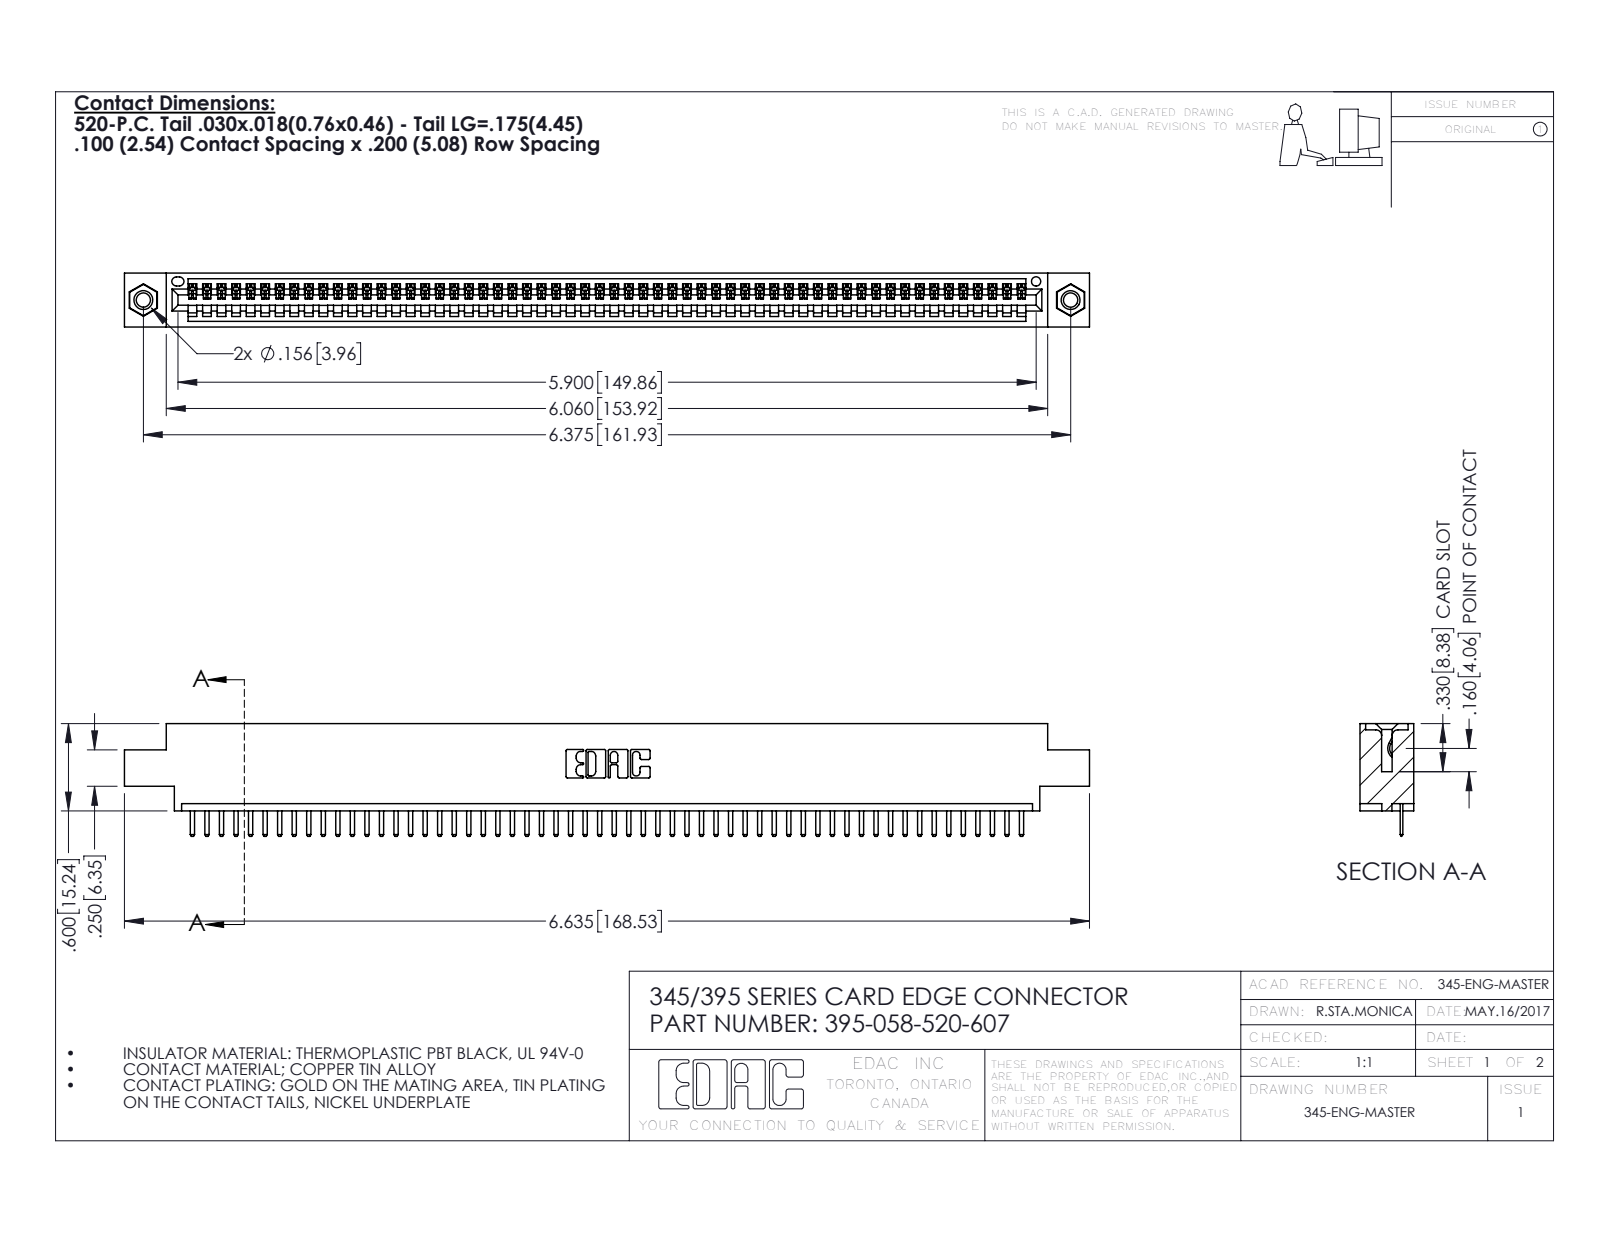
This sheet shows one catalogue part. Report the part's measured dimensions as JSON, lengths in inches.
{"part_name": "345-292-001_345-293-120; 345 Part_0.170 Offset - 0.156 Dia-TI; 345-250-001_345-250-005-103; 395-058-520-607", "step_written_by": "SolidWorks 2016 (CONFIG_CONTROL_DESIGN)", "units": "inches", "bodies": {"solids": 61, "faces": 3786, "planar": 2552, "cylindrical": 1218, "other": 16}, "overall_size": [6.635, 0.775, 0.37], "volume_in3": 0.967, "surface_area_in2": 32.37, "round_holes": [[0.098, 2], [0.125, 2], [0.156, 2], [0.064, 1]], "round_bosses_or_shafts": [[0.155, 2]], "partial_cylinders_radius": [[0.01, 118], [0.006, 116], [0.01, 22], [0.007, 6], [0.031, 6], [0.026, 3], [0.031, 2], [0.04, 2]], "face_to_face_distances": [0.072, 0.298, 0.37, 0.2, 0.098, 0.272, 0.025, 0.225, 0.072, 0.175], "hole_center_spacings": [0.27, 6.139, 6.375]}
